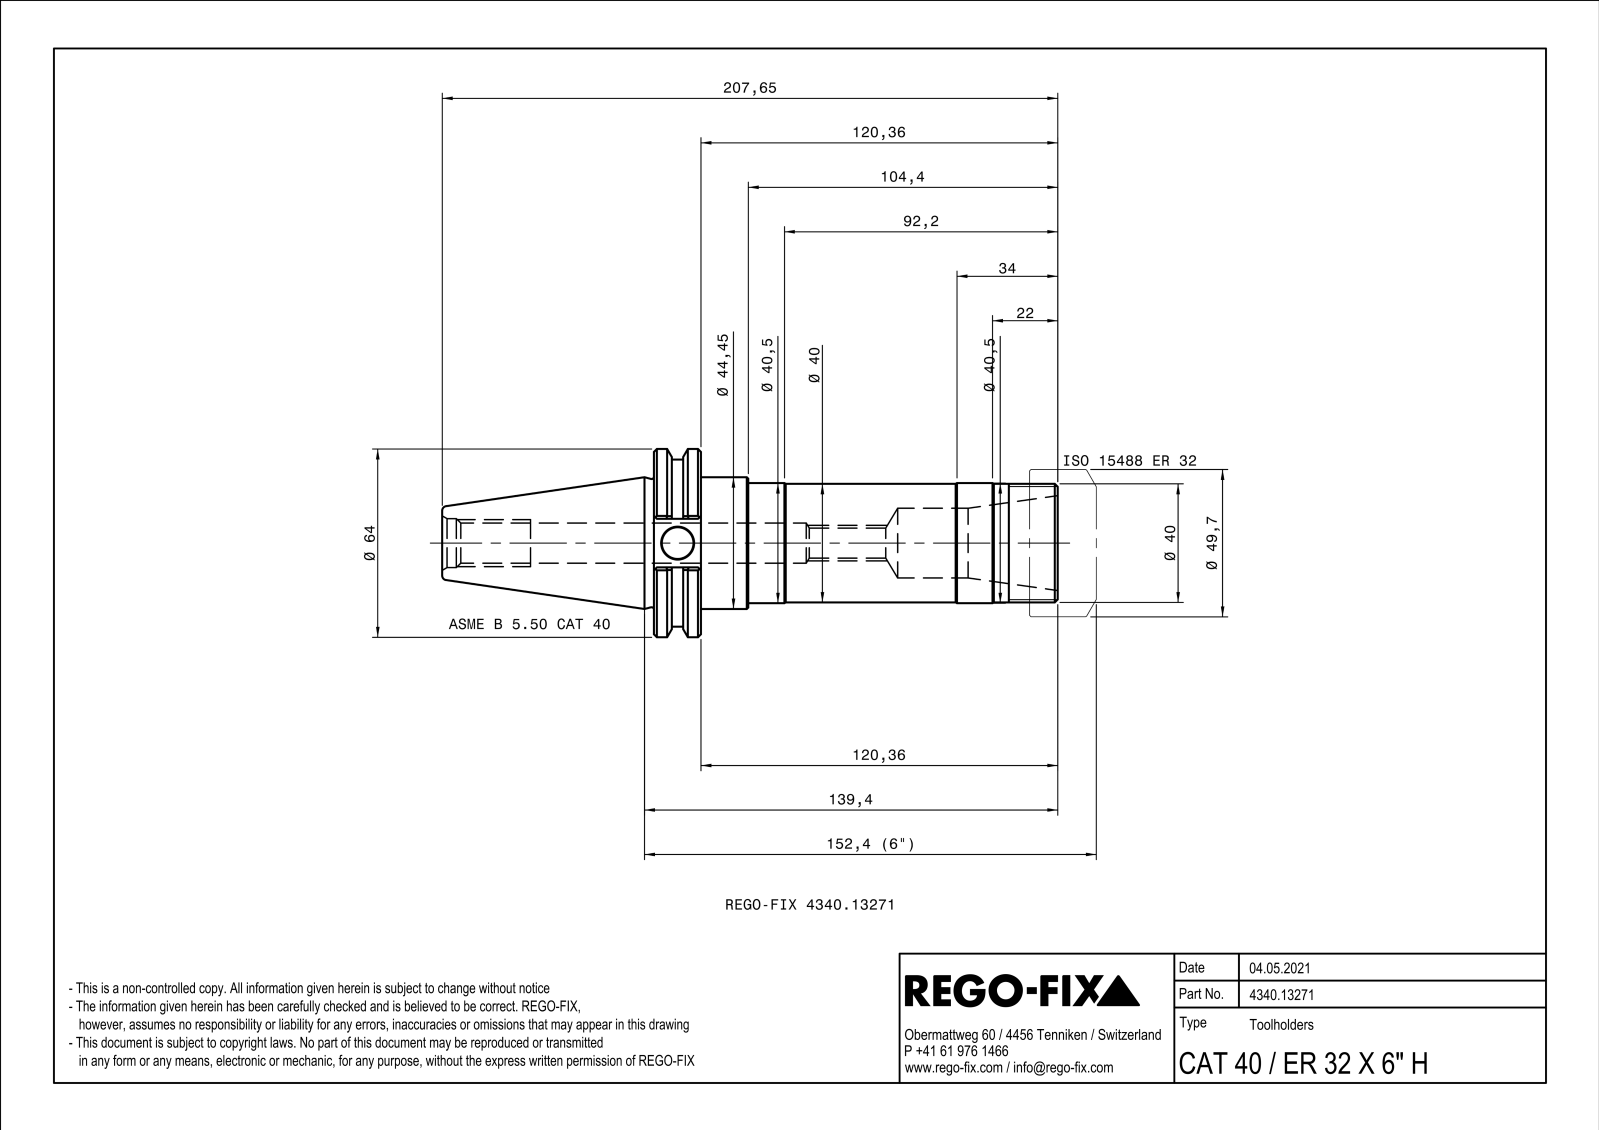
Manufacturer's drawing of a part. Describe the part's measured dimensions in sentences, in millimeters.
The part is named "NOCUT". Its 3-D file was written by "SIEMENS PLM Software Solid Edge ST10 (AUTOMOTIVE_DESIGN)". It is 1 solid with 111 faces: 31 planar, 26 cylindrical and 54 other. Overall it measures 207.65 by 63.5 by 60.79 millimeters. Its volume is 213 627 cubic millimeters and its surface area 42 726 square millimeters. Round holes: 1 of diameter 10.7, 1 of diameter 13.53, 1 of diameter 16.5, 1 of diameter 23.5. Round bosses or shafts: 1 of diameter 63.5, 1 of diameter 56.36, 1 of diameter 44.45, 1 of diameter 40.5, 1 of diameter 40. Partial cylindrical surfaces (rounded edges, fillets, slot ends): 4 of radius 0.5. The main face-to-face distances are 15.87, 120.36, 136.23, 47.33, 16.38, 207.65, 87.29, 71.42, 126.35, 5.99.
